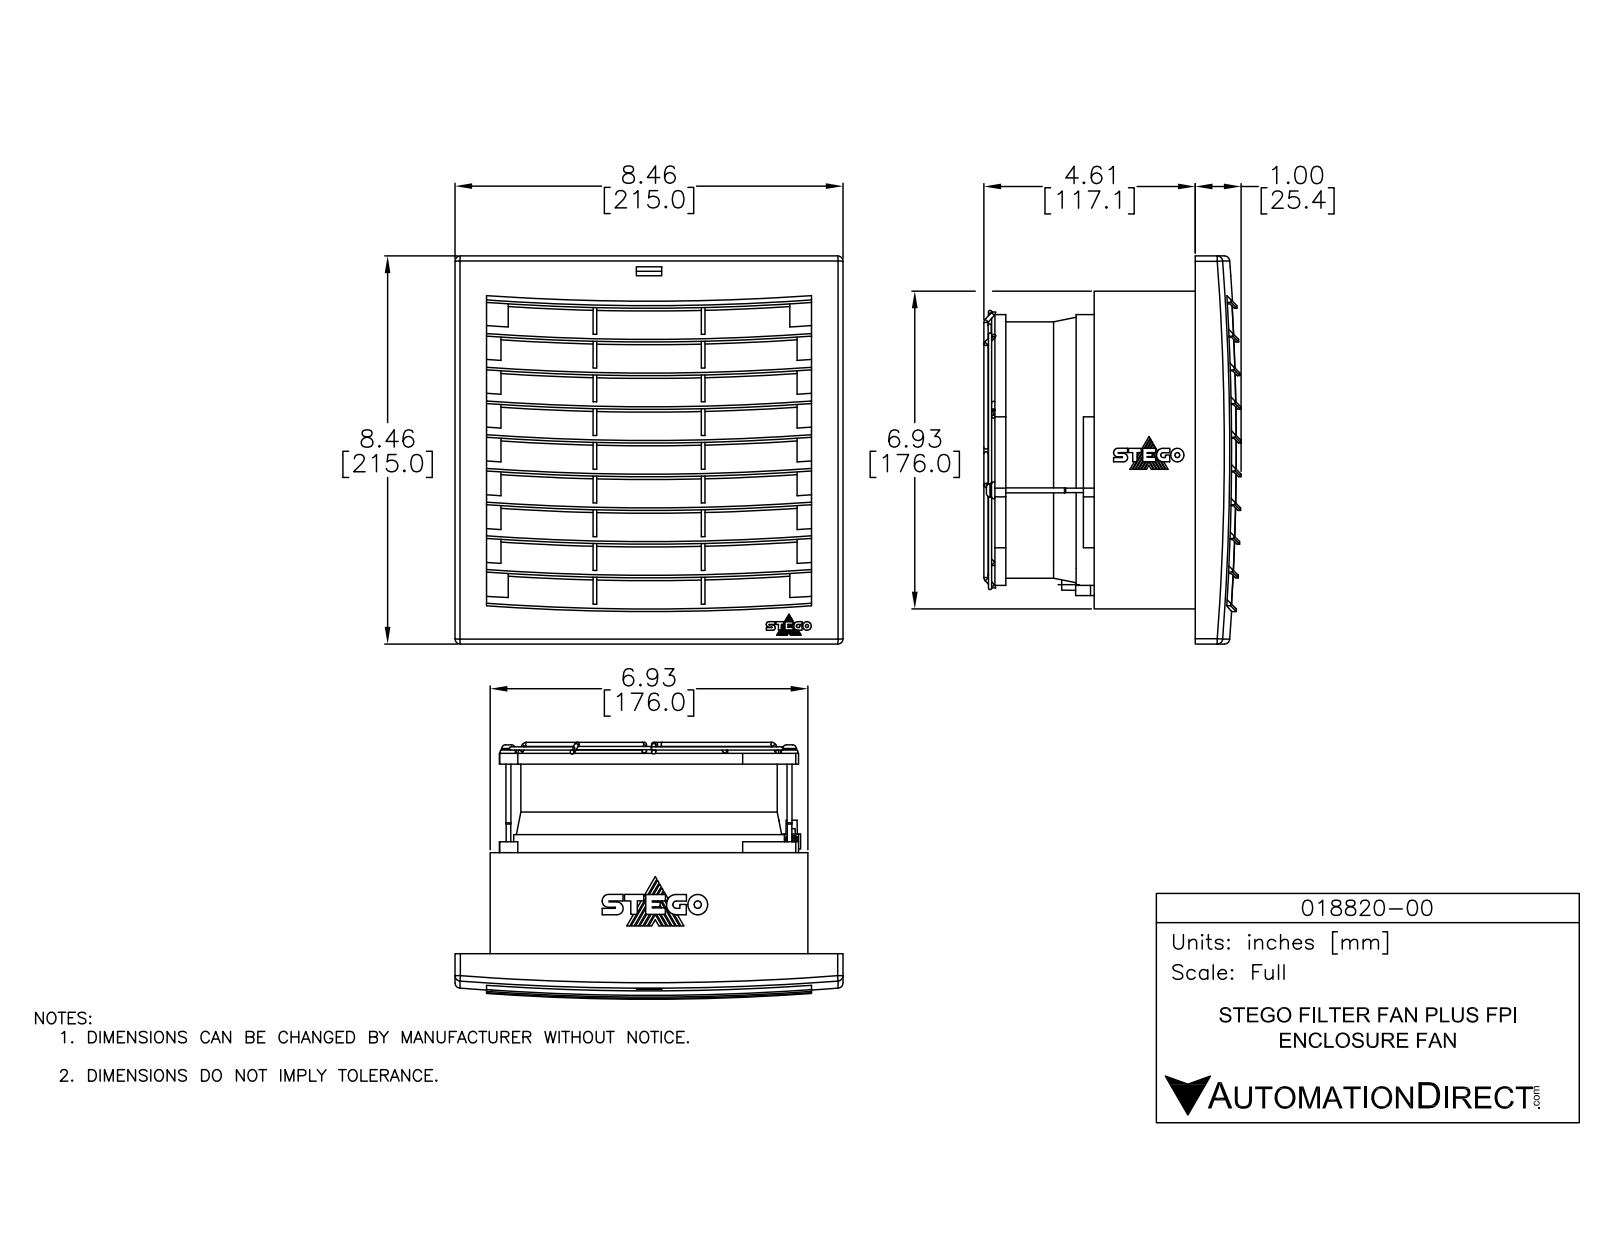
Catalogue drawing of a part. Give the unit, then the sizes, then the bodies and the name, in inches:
Units: inches
Overall size (bounding box): 8.465 × 8.465 × 5.591
Round holes (diameter × count): ⌀1.381 ×1, ⌀2.024 ×1, ⌀2.666 ×1, ⌀3.121 ×1, ⌀3.309 ×1, ⌀3.951 ×1, ⌀4.005 ×1, ⌀4.594 ×1, ⌀4.888 ×1, ⌀5.354 ×1, ⌀5.89 ×1
Round bosses / shafts (diameter × count): ⌀6.358 ×1, ⌀6.024 ×1, ⌀5.124 ×1, ⌀4.83 ×1, ⌀4.241 ×1, ⌀4.187 ×1, ⌀3.545 ×1, ⌀3.357 ×1
Partial cylindrical surfaces — rounded edges, fillets, slot ends (radius × count): R27.614 ×19, R2.463 ×5, R0.197 ×4, R0.201 ×4, R0.551 ×2, R0.736 ×1, R1.119 ×1, R1.237 ×1
Main face-to-face distances: 0.059, 0.941, 0.191, 1.881, 0.118, 0.173, 6.756, 0.47, 0.47, 1
Volume: 76.88 in³ · Surface area: 680.2 in²
Bodies: 1 solid, 795 faces (460 planar, 333 cylindrical, 2 other)
Part name (STEP PRODUCT): 018820-00
STEP written by: SolidWorks 2017 (AUTOMOTIVE_DESIGN)
